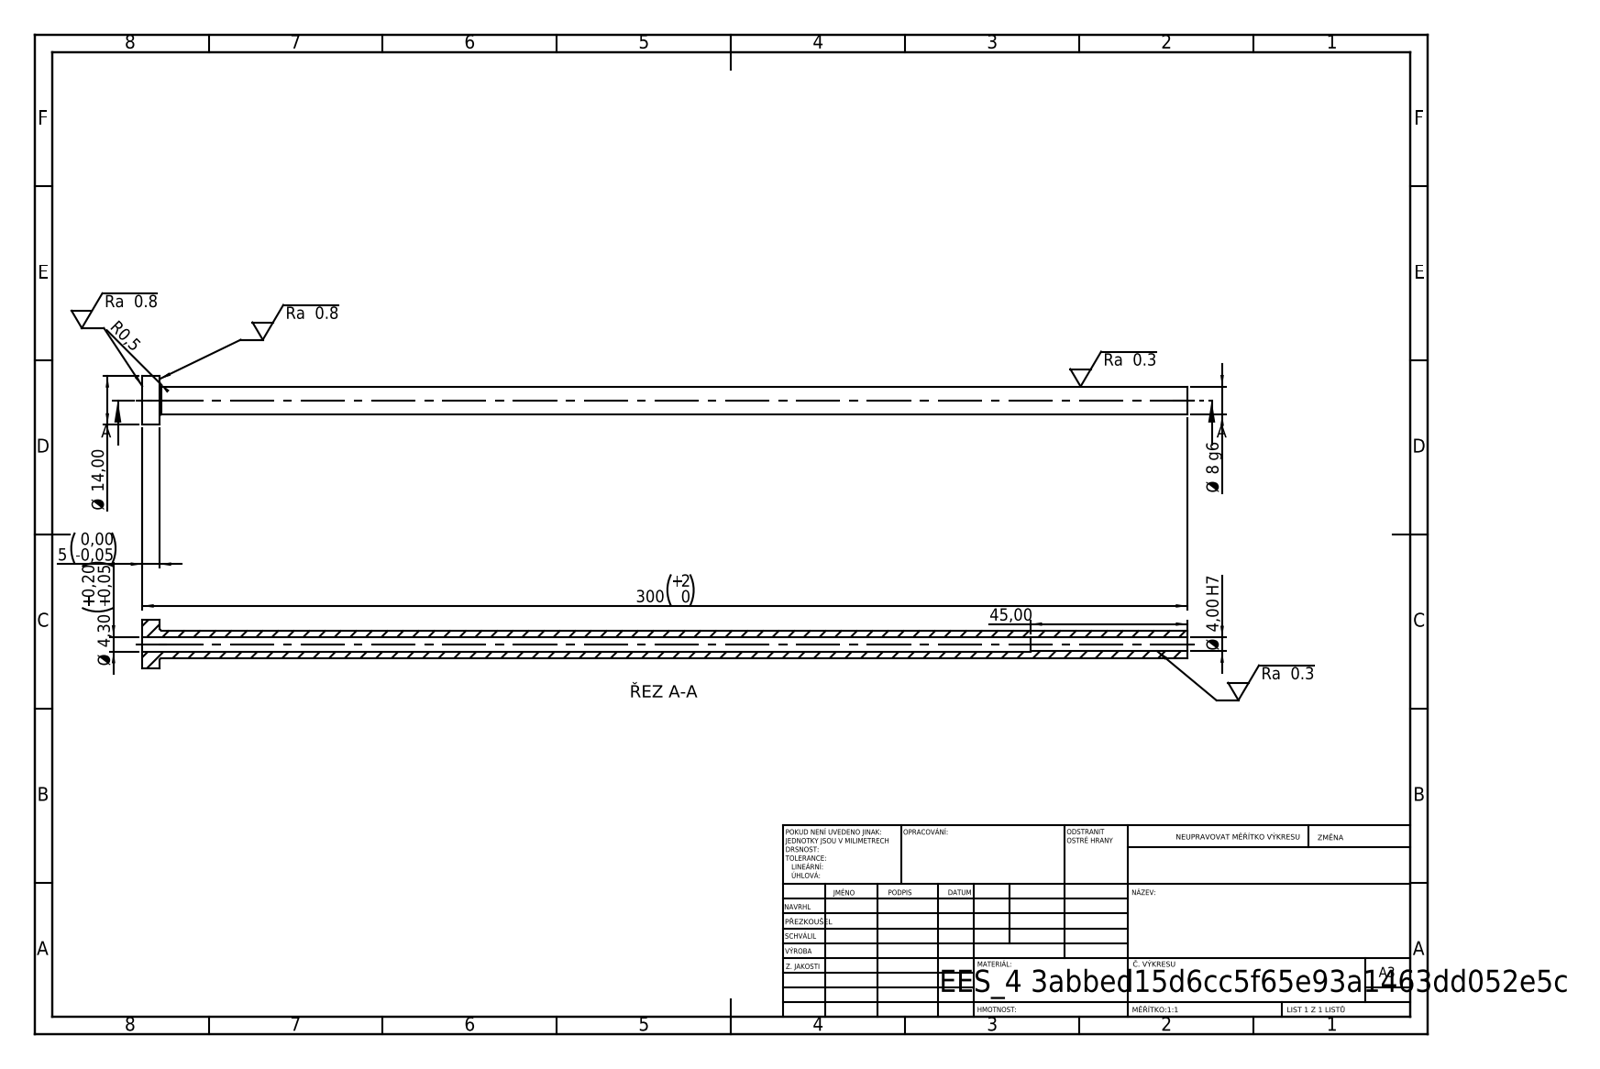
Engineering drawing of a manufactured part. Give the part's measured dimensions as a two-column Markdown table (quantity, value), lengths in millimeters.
| quantity | value |
| --- | --- |
| STEP written by | SolidWorks 2019 (CONFIG_CONTROL_DESIGN) |
| units | millimeters |
| bodies | 1 solid, 14 faces (4 planar, 8 cylindrical, 2 other) |
| overall size | 300 × 14 × 14 |
| volume | 11 331 mm³ |
| surface area | 11 922 mm² |
| round holes (diameter × count) | 4 × 1, 4.3 × 1 |
| round bosses / shafts (diameter × count) | 14 × 1, 8 × 1 |
| main face-to-face distances | 5, 300, 295, 255, 250, 45 |
